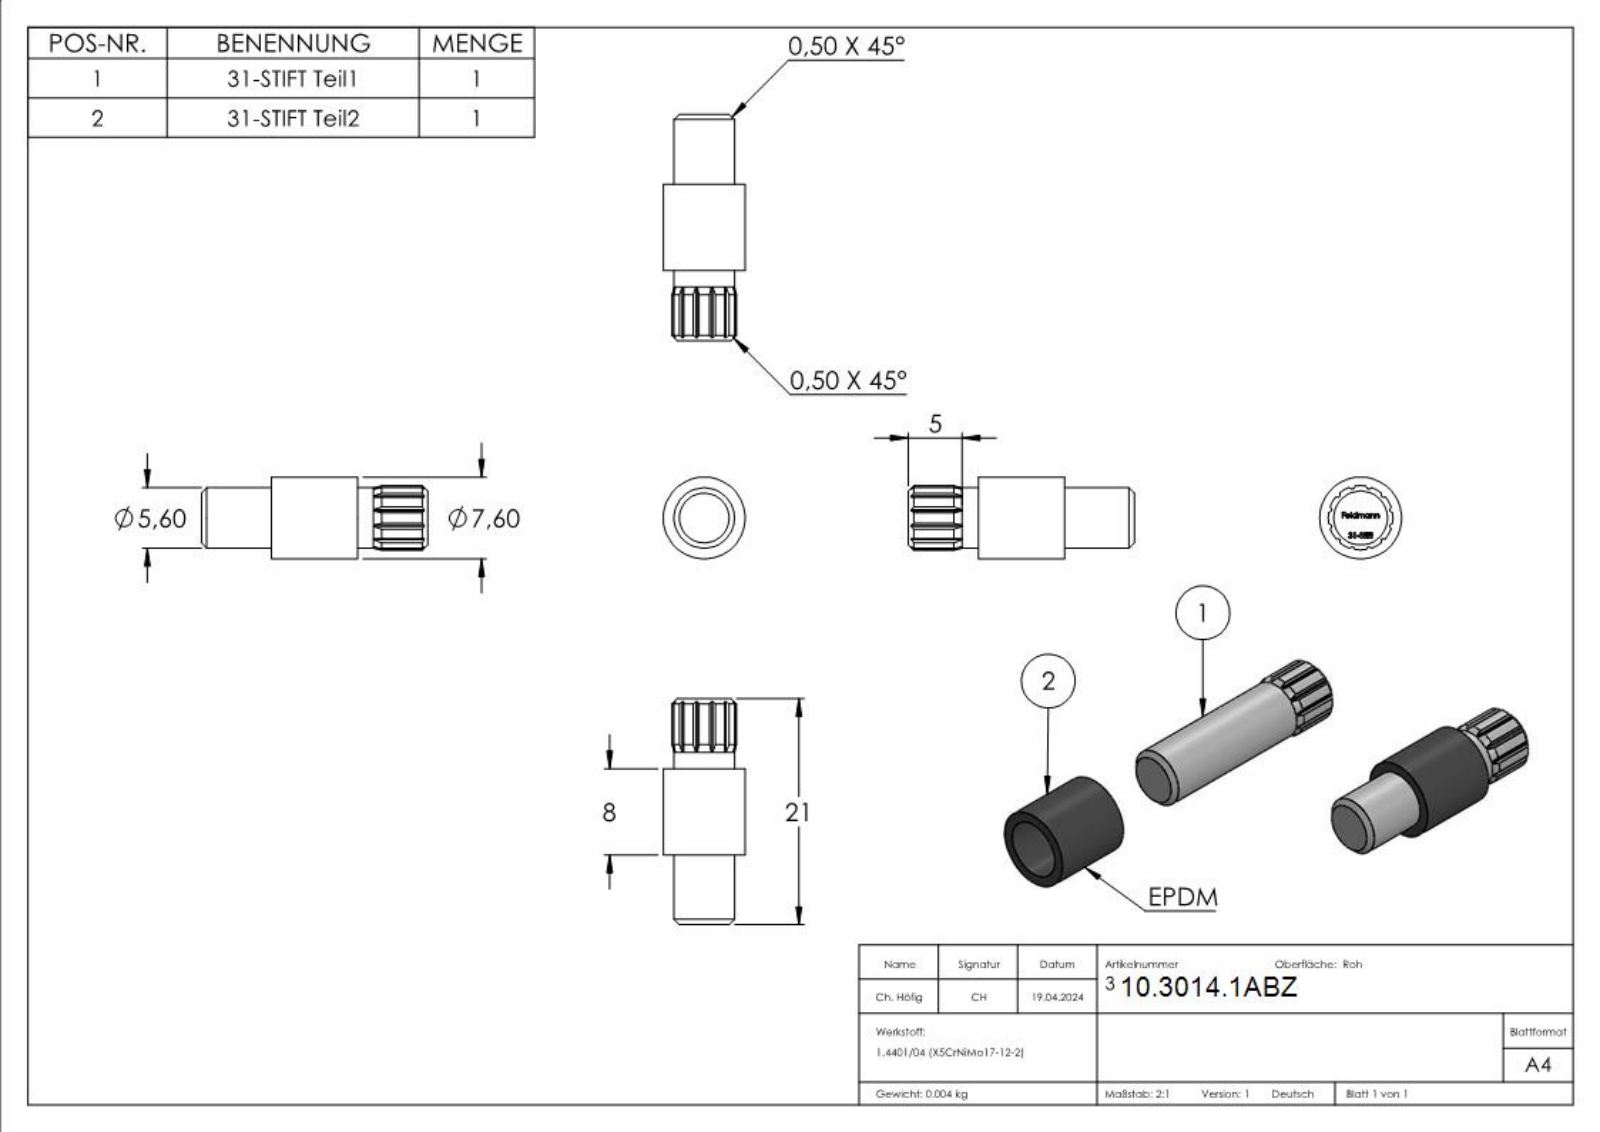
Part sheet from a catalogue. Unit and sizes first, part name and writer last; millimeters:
Units: millimetres
Overall size (bounding box): 21 × 7.6 × 7.6
Round holes (diameter × count): ⌀5.6 ×1
Round bosses / shafts (diameter × count): ⌀7.6 ×1
Partial cylindrical surfaces — rounded edges, fillets, slot ends (radius × count): R3 ×1
Main face-to-face distances: 6.5, 14.5, 8, 21, 4.03, 4.04, 6.4, 14.4, 20.9, 0.63
Volume: 692 mm³ · Surface area: 801 mm²
Bodies: 2 solids, 278 faces (157 planar, 19 cylindrical, 102 other)
Part name (STEP PRODUCT): 31-Stift Teil2; 31-Stift; 31-Stift Teil1
STEP written by: SolidWorks 2015 (CONFIG_CONTROL_DESIGN)
